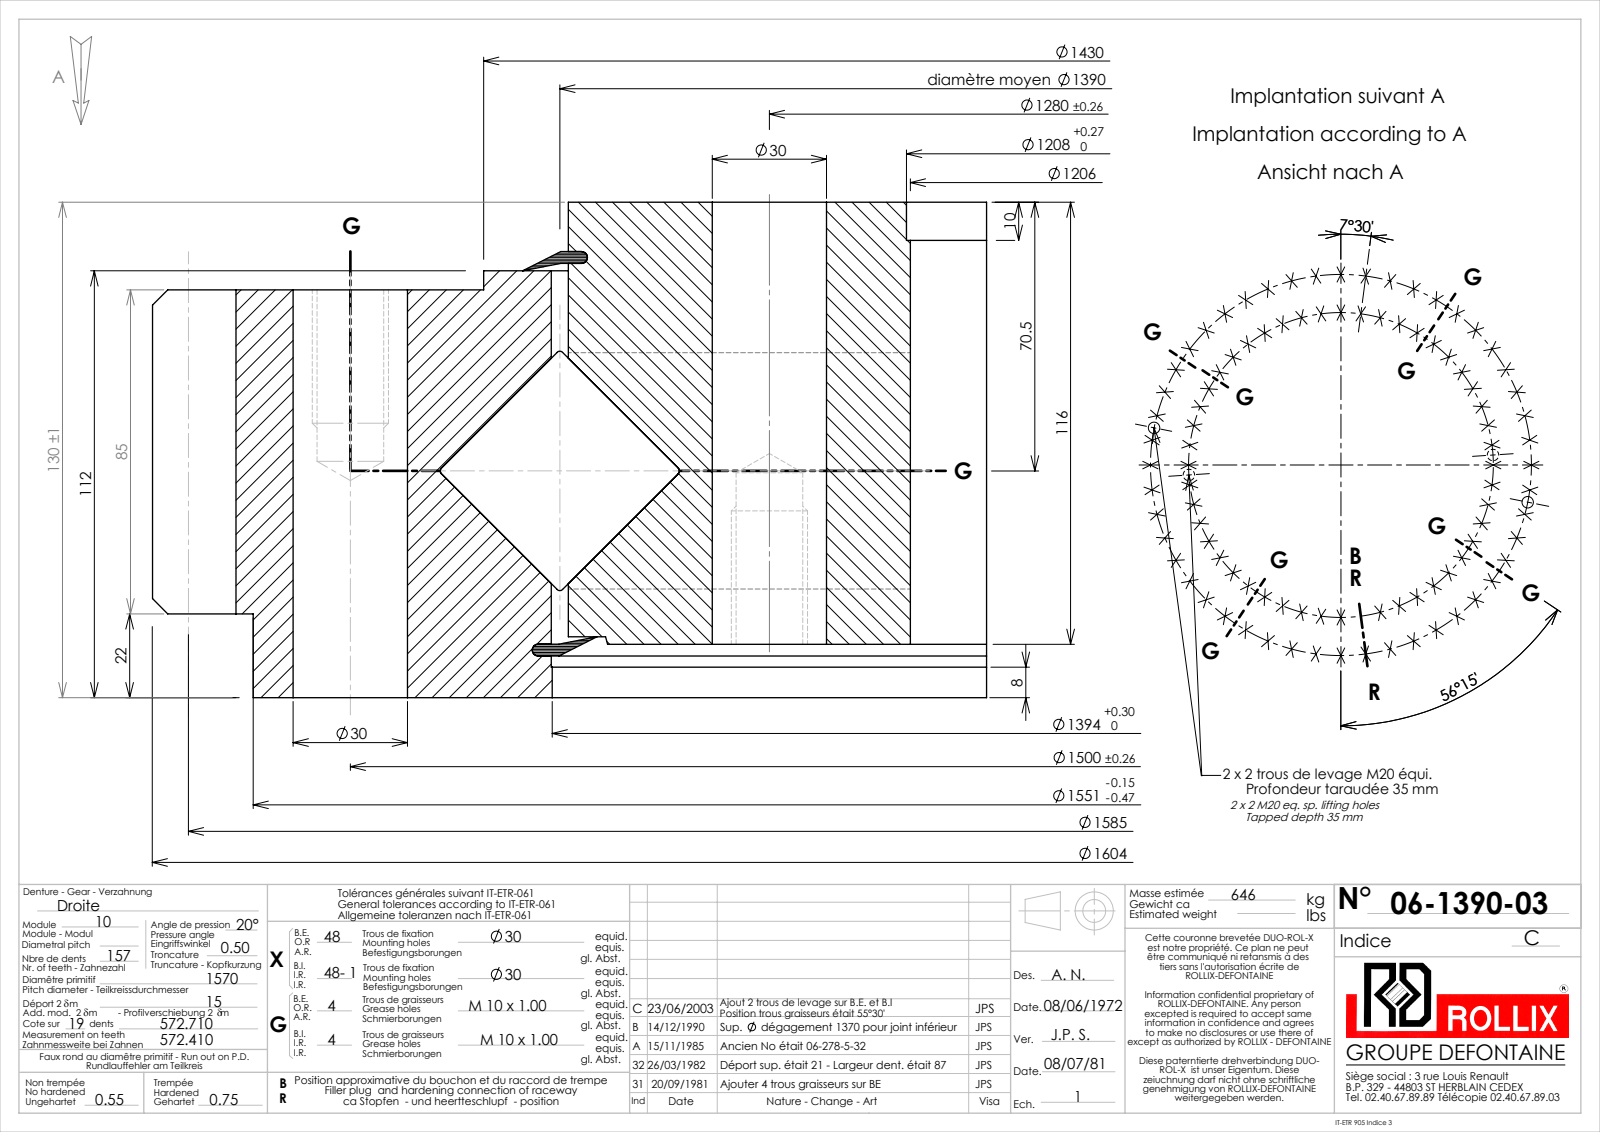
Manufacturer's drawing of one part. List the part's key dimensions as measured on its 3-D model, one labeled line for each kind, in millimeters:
Part name (STEP PRODUCT): 06-1390-03
STEP written by: SolidWorks 2016 (CONFIG_CONTROL_DESIGN)
Units: millimetres
Bodies: 5 solids, 1263 faces (333 planar, 553 cylindrical, 377 other)
Overall size (bounding box): 1603.99 × 1603.92 × 130
Volume: 73 270 000 mm³ · Surface area: 5 509 000 mm²
Round holes (diameter × count): ⌀30 ×95, ⌀9 ×8, ⌀17.5 ×4, ⌀1206 ×1, ⌀1208 ×1, ⌀1394 ×1, ⌀1394.5 ×1
Round bosses / shafts (diameter × count): ⌀1551 ×1, ⌀1430 ×1, ⌀1385.5 ×1, ⌀45 ×1
Partial cylindrical surfaces — rounded edges, fillets, slot ends (radius × count): R780 ×1, R802 ×1
Main face-to-face distances: 130, 107, 23, 14, 93, 116, 98, 112, 8, 5
Hole centre spacings: 195.79, 750, 913.14, 98.1, 292.63, 388.23, 574.03, 1060.66
